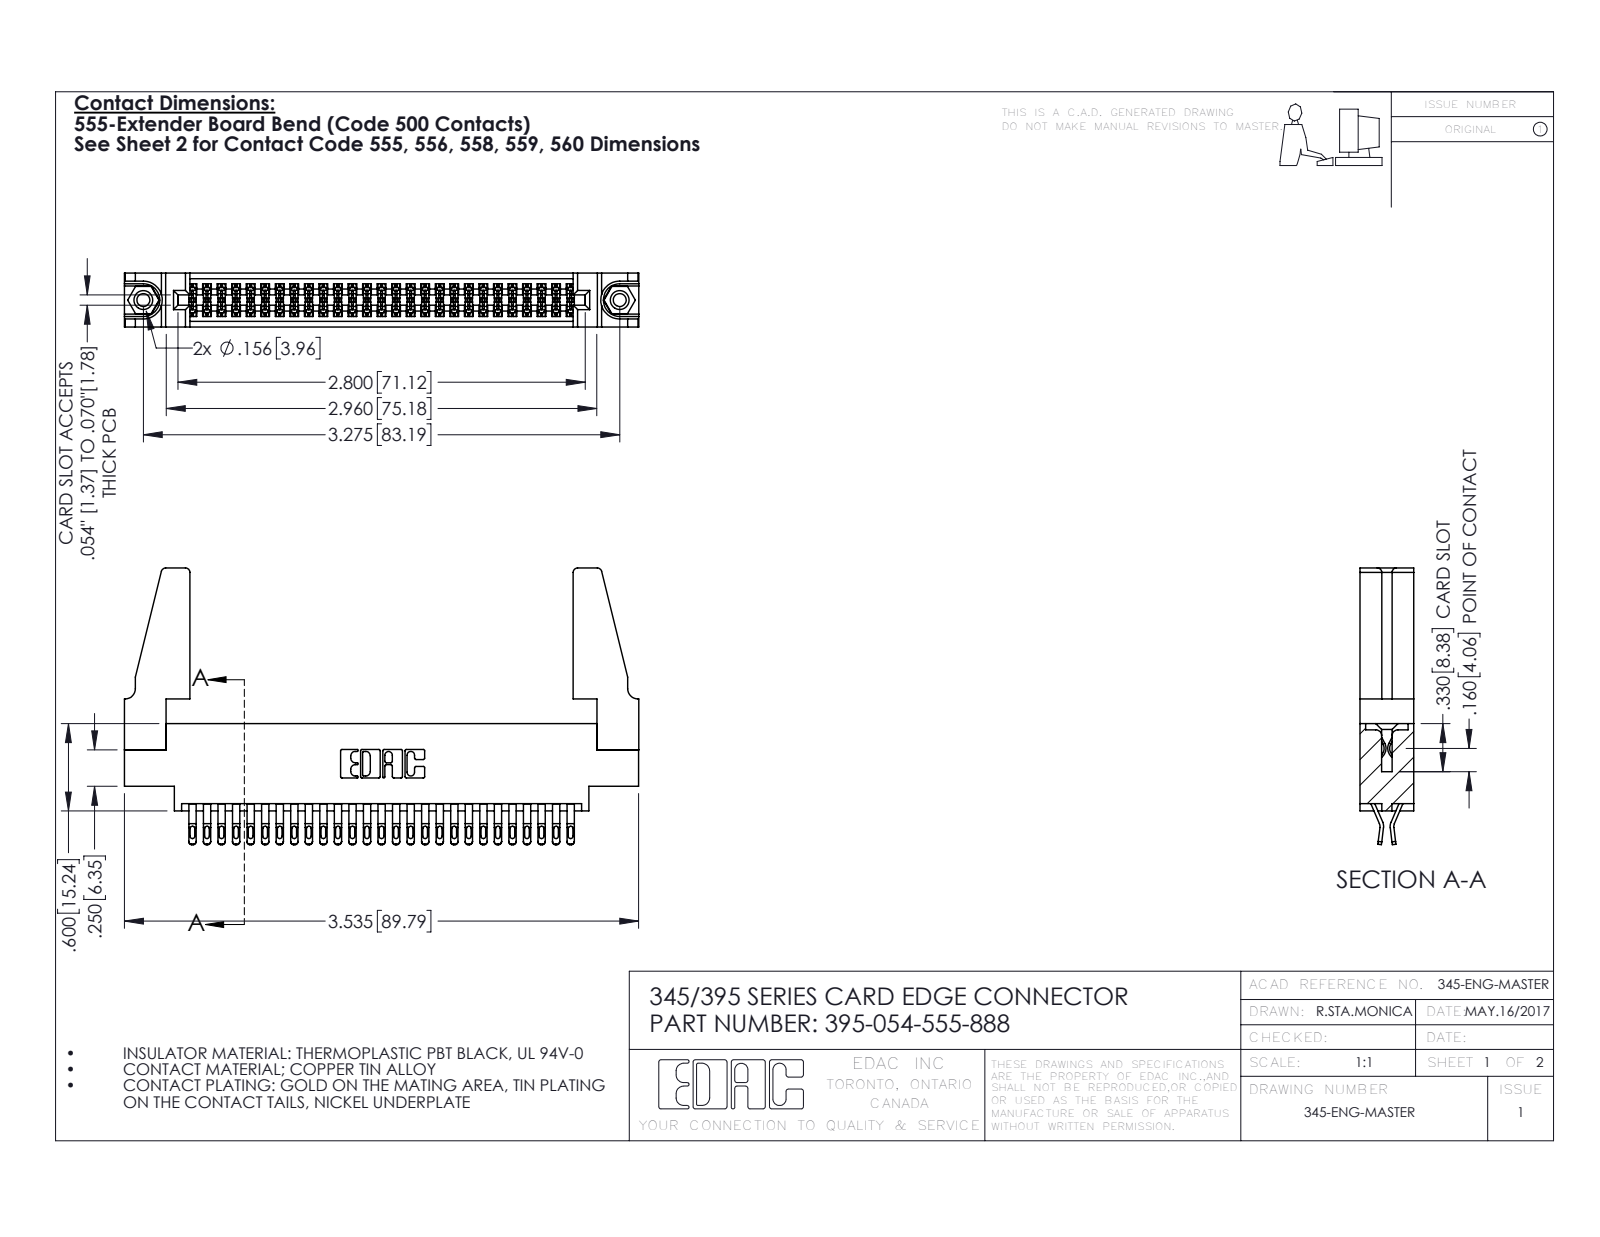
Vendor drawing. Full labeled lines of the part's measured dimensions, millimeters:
Part name (STEP PRODUCT): 345-220-078_345-220-088; 345-250-001_345-250-001-102; 395-054-555-888; 345 Part_0.170 Offset - 0.156 Dia-TH (+1 more)
STEP written by: SolidWorks 2016 (CONFIG_CONTROL_DESIGN)
Units: millimetres
Bodies: 59 solids, 3278 faces (1830 planar, 1432 cylindrical, 16 other)
Overall size (bounding box): 89.8 × 48.3 × 9.4
Volume: 11 900 mm³ · Surface area: 16 280 mm²
Round holes (diameter × count): ⌀2.3 ×2, ⌀3.2 ×2, ⌀4 ×2, ⌀1.6 ×1
Round bosses / shafts (diameter × count): ⌀3.9 ×2
Partial cylindrical surfaces — rounded edges, fillets, slot ends (radius × count): R0.4 ×135, R0.5 ×108, R0.2 ×81, R0.3 ×22, R0.8 ×8, R0.2 ×6, R0.8 ×6, R0.7 ×3
Main face-to-face distances: 9.4, 1.8, 7.6, 0.6, 5.1, 2.5, 6.9, 5.7, 4.4, 3.8
Hole centre spacings: 6.9, 77.2, 83.2
